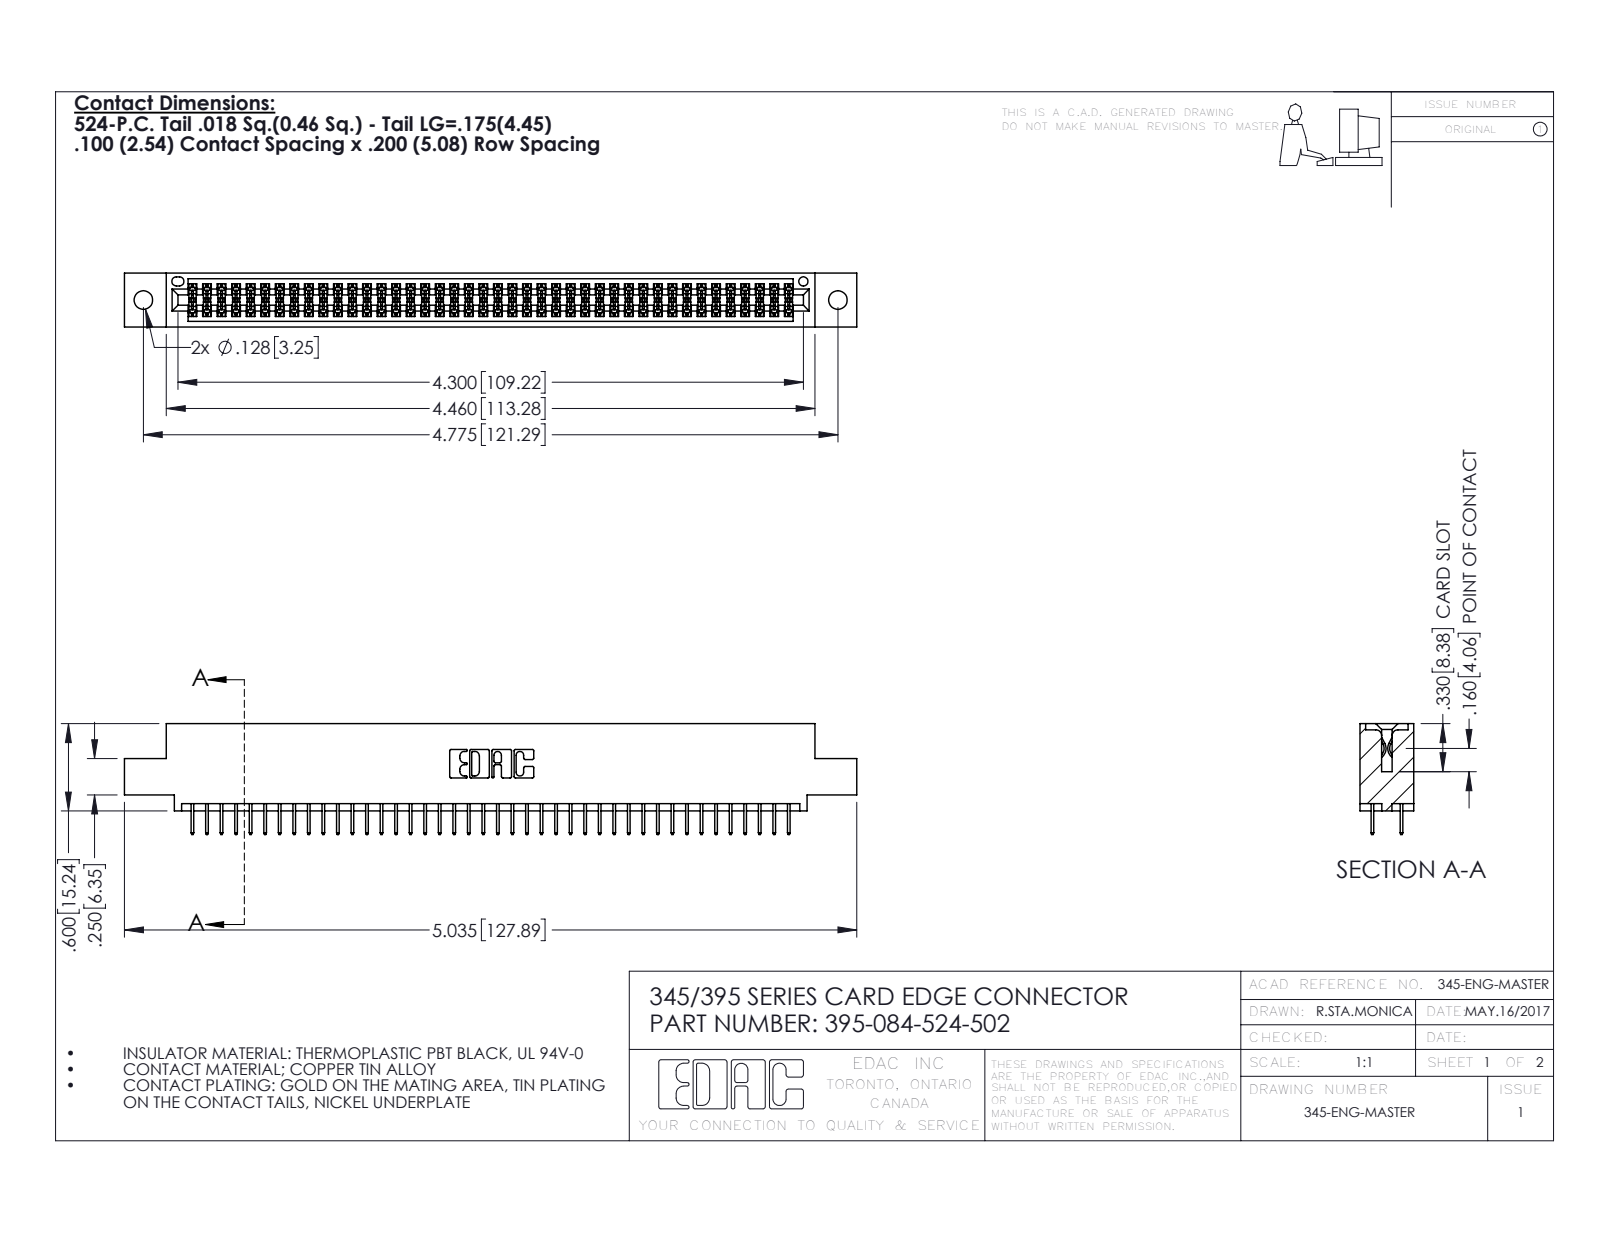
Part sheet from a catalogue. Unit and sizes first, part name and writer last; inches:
Units: inches
Overall size (bounding box): 5.035 × 0.762 × 0.37
Round holes (diameter × count): ⌀0.128 ×2, ⌀0.064 ×1
Partial cylindrical surfaces — rounded edges, fillets, slot ends (radius × count): R0.006 ×126, R0.01 ×22, R0.007 ×6, R0.031 ×6, R0.026 ×3, R0.014 ×2, R0.019 ×2, R0.022 ×2
Main face-to-face distances: 0.072, 0.298, 0.2, 0.37, 0.098, 0.272, 0.025, 0.225, 0.072, 0.175
Hole centre spacings: 0.27, 4.539, 4.775
Volume: 0.744 in³ · Surface area: 27.12 in²
Bodies: 85 solids, 4666 faces (3360 planar, 1306 cylindrical, 0 other)
Part name (STEP PRODUCT): 345-292-001_345-293-124; 345 Part_0.110 Offset - 0.128 Dia; 395-084-524-502
STEP written by: SolidWorks 2016 (CONFIG_CONTROL_DESIGN)
